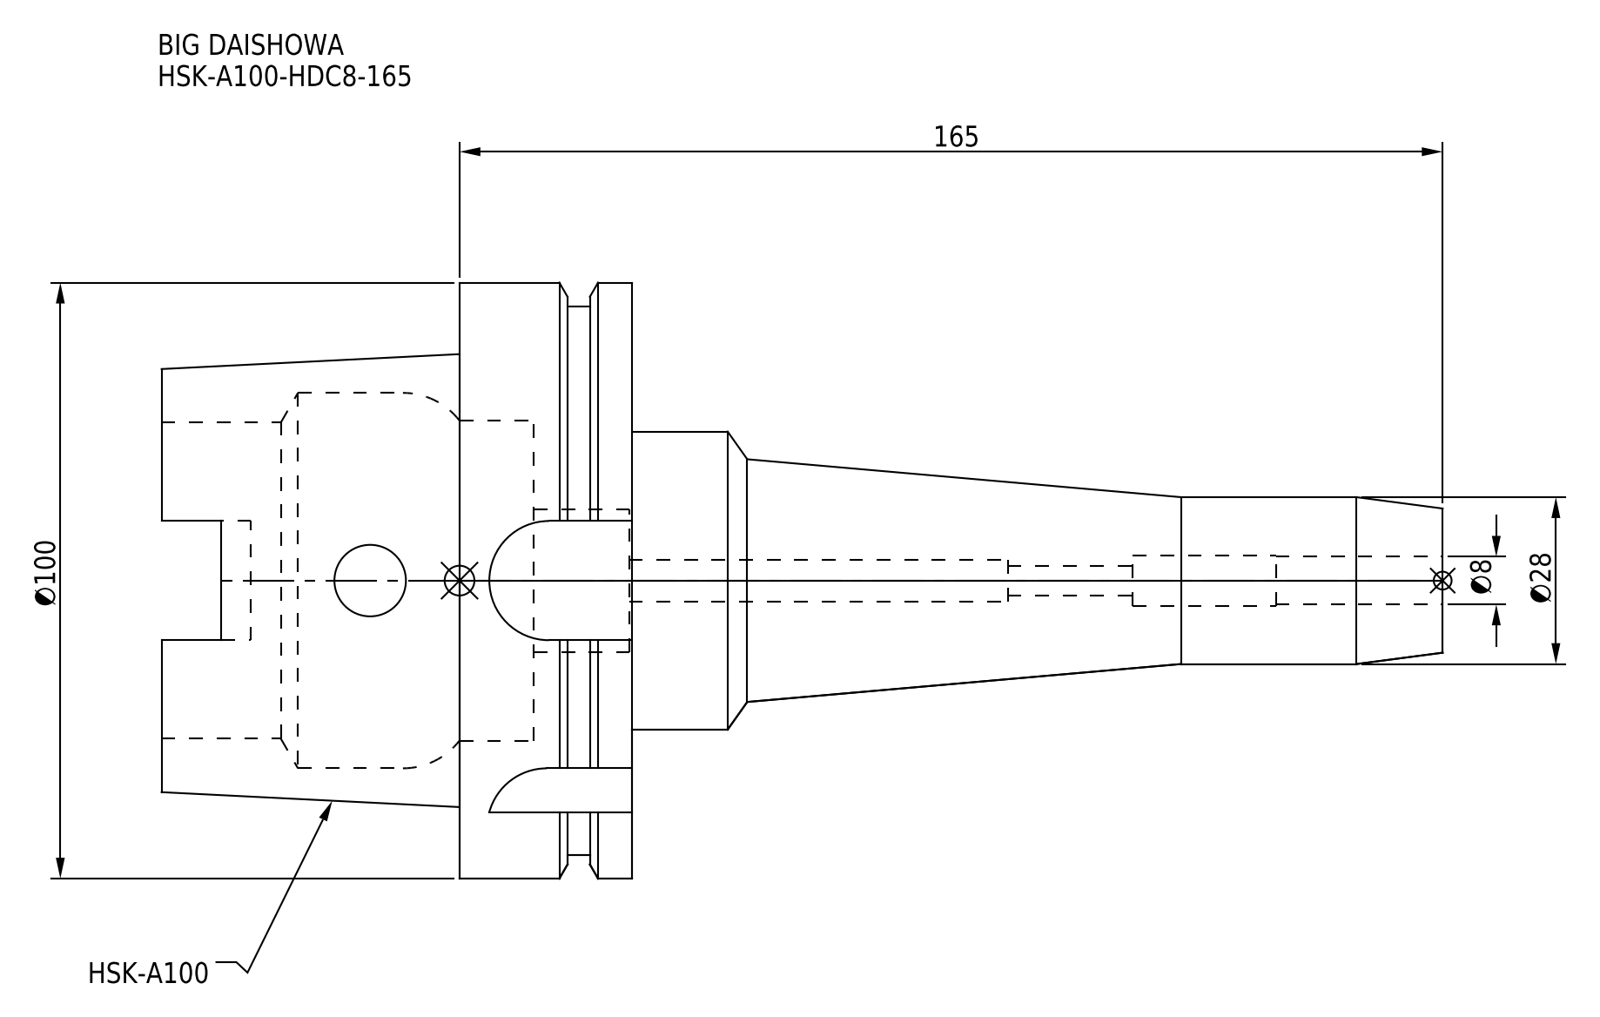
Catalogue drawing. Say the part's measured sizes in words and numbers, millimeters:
The part is named "HSK-A100-HDC8-165". Its 3-D file was written by "CREO PARAMETRIC BY PTC INC, 2016380 (AUTOMOTIVE_DESIGN)". It is 1 solid with 97 faces: 35 planar, 42 cylindrical and 20 other. Overall it measures 215 by 100 by 100 millimeters. Its volume is 378 779 cubic millimeters and its surface area 66 534 square millimeters. Round holes: 1 of diameter 5, 1 of diameter 7, 1 of diameter 8, 1 of diameter 8.5, 1 of diameter 12, 1 of diameter 24, 1 of diameter 53, 1 of diameter 53.8, 1 of diameter 63. Round bosses or shafts: 1 of diameter 100, 1 of diameter 92, 1 of diameter 50, 1 of diameter 28. Partial cylindrical surfaces (rounded edges, fillets, slot ends): 4 of radius 4.88, 4 of radius 10. The main face-to-face distances are 29, 16.55, 12.45, 79, 62.45, 50, 88, 0.55, 16, 28.45.
